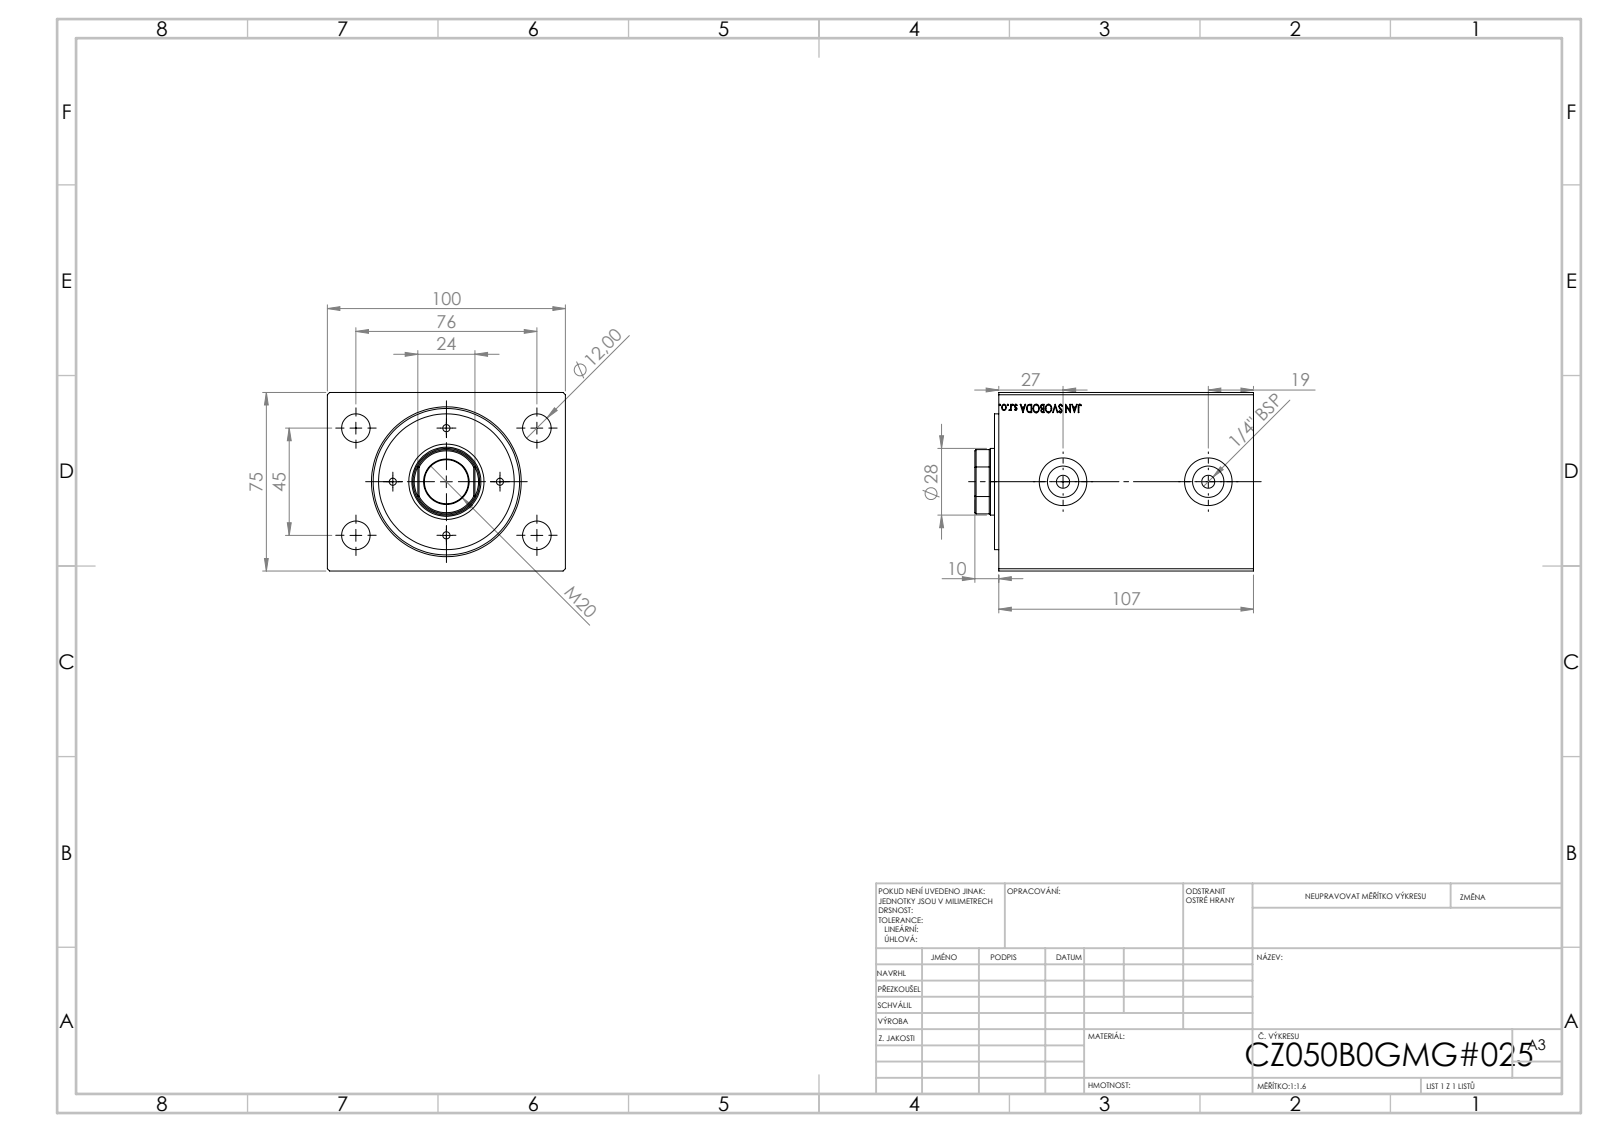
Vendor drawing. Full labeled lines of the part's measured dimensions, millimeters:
Part name (STEP PRODUCT): V500CZ; V500CZ_B_VC
STEP written by: SolidWorks 2019 (CONFIG_CONTROL_DESIGN)
Units: millimetres
Bodies: 3 solids, 873 faces (399 planar, 58 cylindrical, 416 other)
Overall size (bounding box): 117 × 100 × 75
Volume: 811 131 mm³ · Surface area: 122 932 mm²
Round holes (diameter × count): ⌀3 ×4, ⌀12 ×4, ⌀5.5 ×2, ⌀13.16 ×2, ⌀20 ×2, ⌀18.5 ×1, ⌀28 ×1, ⌀29 ×1, ⌀36 ×1, ⌀50 ×1, ⌀61.5 ×1
Round bosses / shafts (diameter × count): ⌀57 ×1
Partial cylindrical surfaces — rounded edges, fillets, slot ends (radius × count): R13.5 ×1
Main face-to-face distances: 75, 100, 107, 89.5, 17.5, 82, 7.5, 25, 91.3, 1.8
Hole centre spacings: 22.5, 27.32, 31.82, 38, 44.16, 45, 58.9, 64.55
